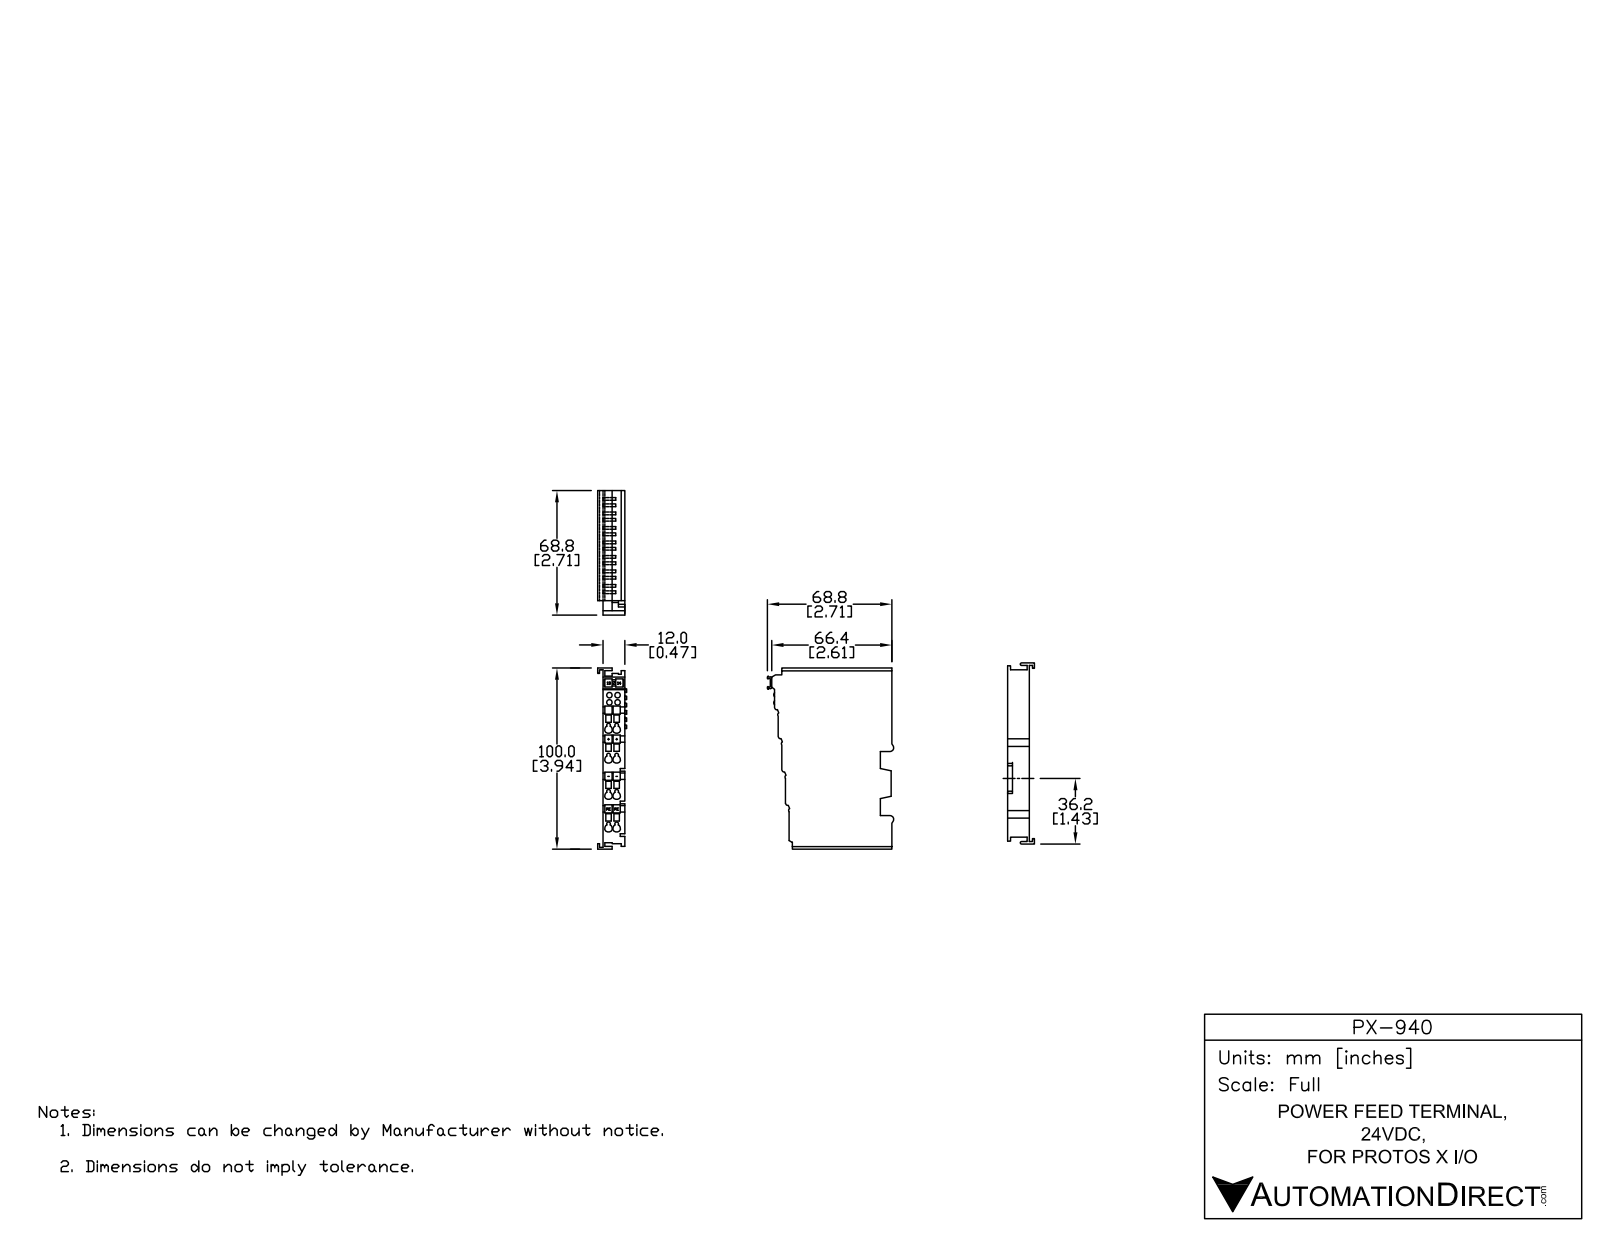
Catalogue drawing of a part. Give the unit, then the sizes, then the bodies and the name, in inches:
Units: inches
Overall size (bounding box): 3.947 × 2.806 × 0.596
Round holes (diameter × count): ⌀0.157 ×8, ⌀0.138 ×4
Partial cylindrical surfaces — rounded edges, fillets, slot ends (radius × count): R0.012 ×46, R0.01 ×35, R0.015 ×12, R0.005 ×10, R0.039 ×9, R0.016 ×8, R0.007 ×4, R0.041 ×4
Main face-to-face distances: 0.472, 0.039, 0.079, 0.394, 0.073, 0.433, 0.343, 0.157, 0.124, 0.048
Hole centre spacings: 0.177, 0.197, 0.724, 0.751, 0.25, 0.63, 0.66, 0.804
Volume: 3.564 in³ · Surface area: 52.52 in²
Bodies: 28 solids, 1367 faces (963 planar, 344 cylindrical, 60 other)
Part name (STEP PRODUCT): PX-940
STEP written by: SolidWorks 2014 (AUTOMOTIVE_DESIGN)
